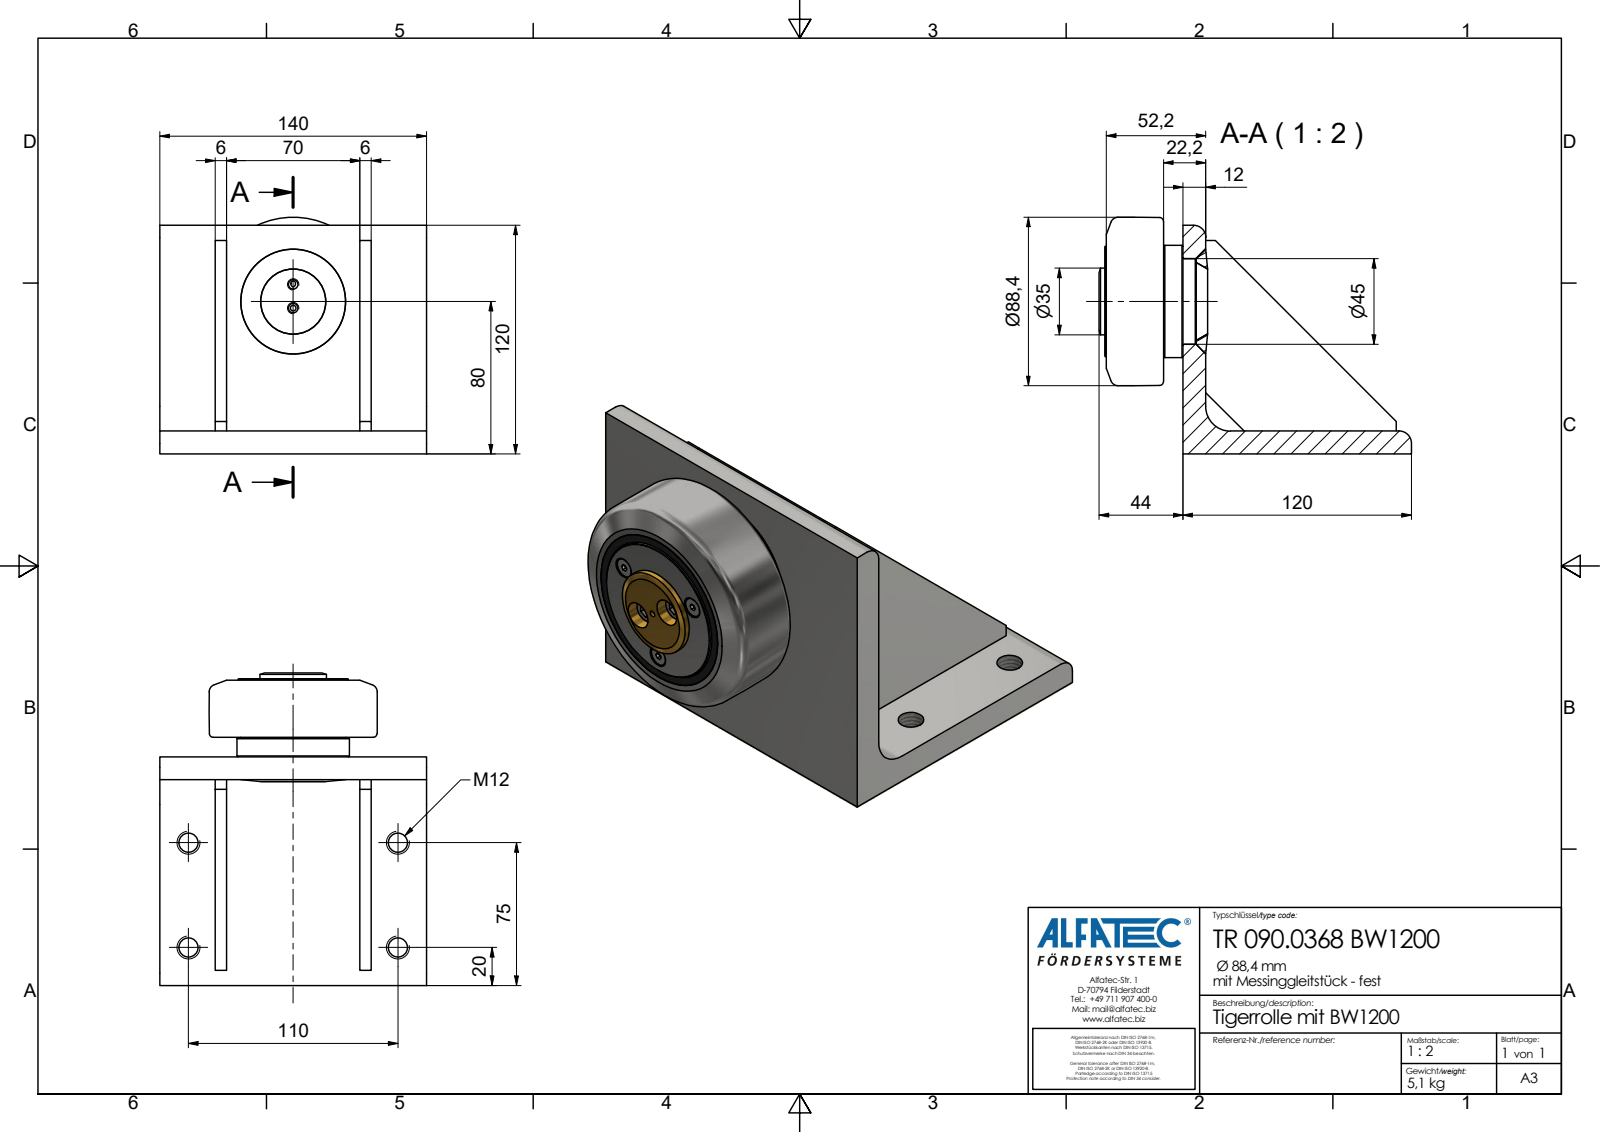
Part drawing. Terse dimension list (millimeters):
name: TR 090.0368 BW1200_Kontur
written by: Autodesk Inventor 2020 (AP242_MANAGED_MODEL_BASED_3D_ENGINEERING_MIM_LF)
unit: mm
bodies: 1 solid, 96 faces (58 planar, 24 cylindrical, 14 other)
size: 164 × 140 × 124.2
volume: 657 065 mm³; area: 111 225 mm²
holes: 4× ⌀10.11, 3× ⌀8.6, 2× ⌀2.5, 2× ⌀4.92, 2× ⌀11, 1× ⌀3
bosses: 3× ⌀7.8, 1× ⌀59, 1× ⌀57.8, 1× ⌀55.3, 1× ⌀35
rounds: 2× R6.5, 1× R13
face distances: 12, 76, 6, 29, 35, 105, 111, 82, 70, 10.2
hole spacings: 22, 38.1, 9.25, 19.15, 23.94, 27.8, 55, 110
